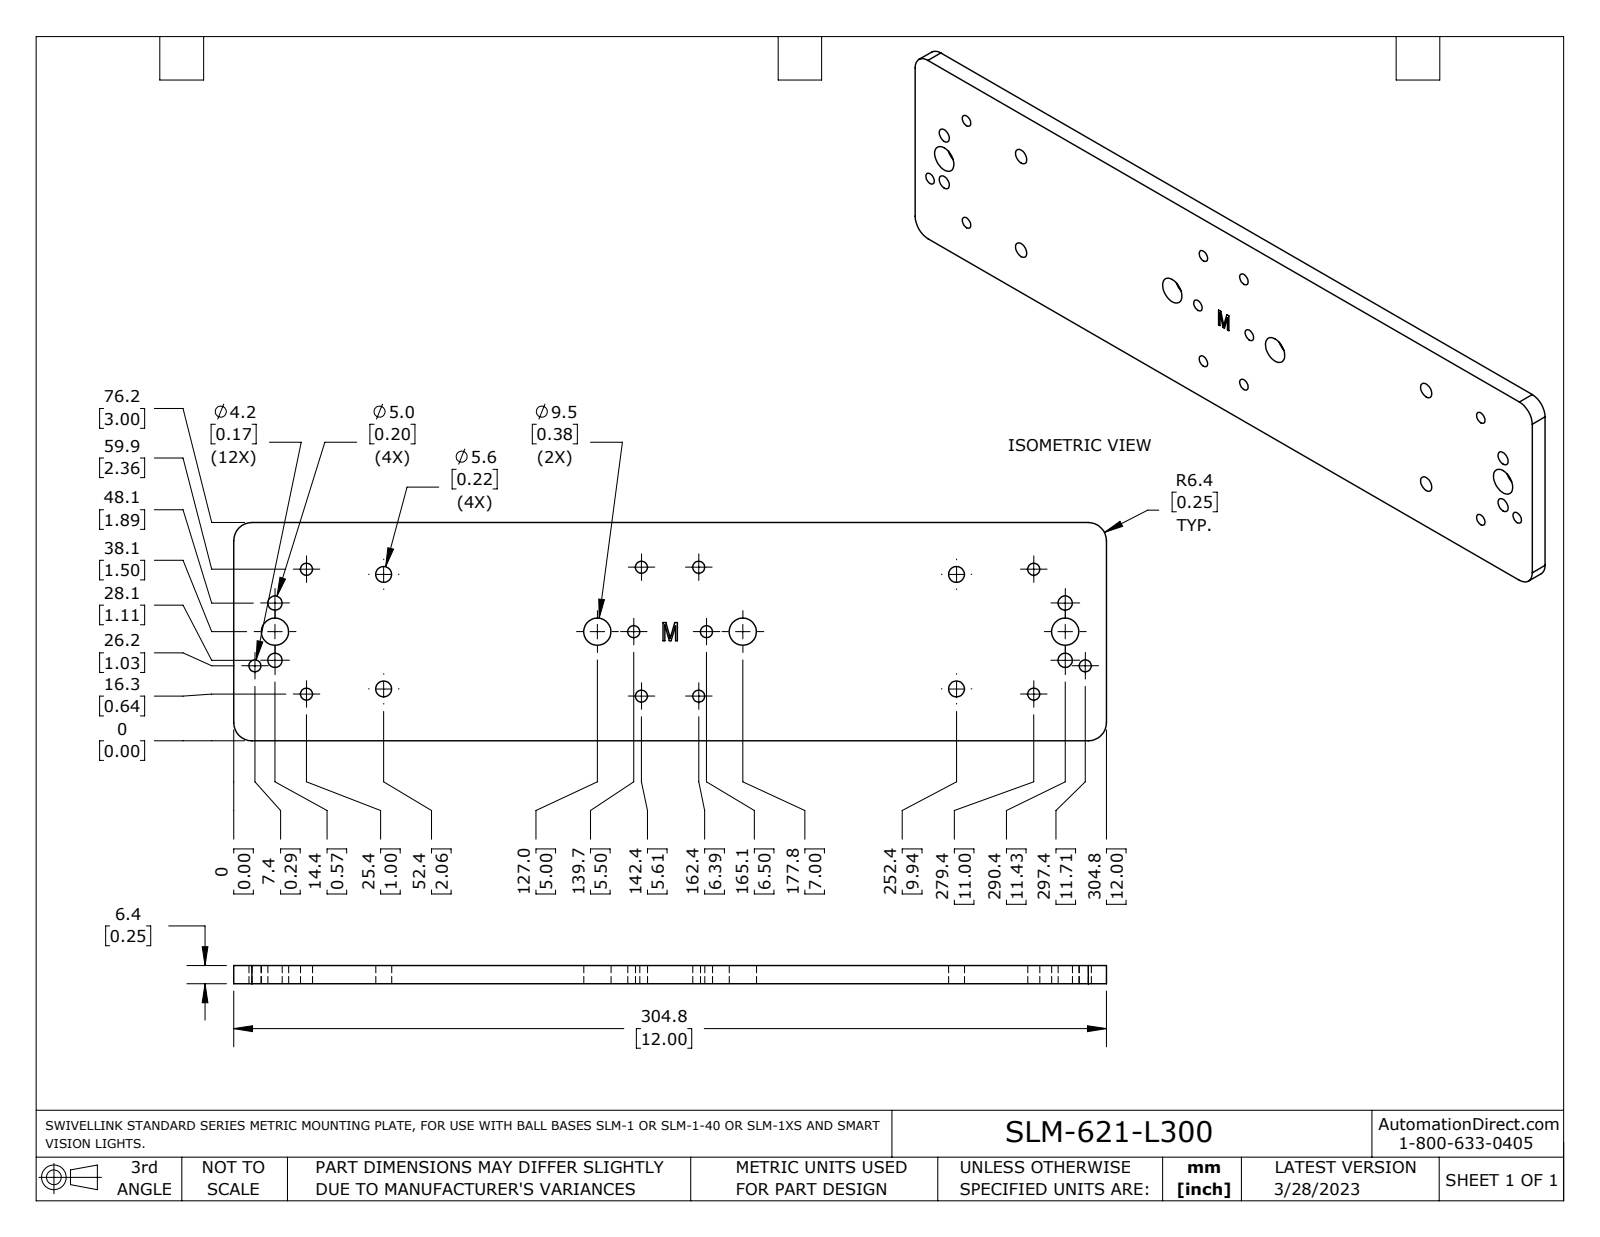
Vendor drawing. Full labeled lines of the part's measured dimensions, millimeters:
Part name (STEP PRODUCT): SLM-621-L300
STEP written by: SolidWorks 2021 (AUTOMOTIVE_DESIGN)
Units: millimetres
Bodies: 1 solid, 35 faces (7 planar, 28 cylindrical, 0 other)
Overall size (bounding box): 304.8 × 76.2 × 6.4
Volume: 143 300 mm³ · Surface area: 52 500 mm²
Round holes (diameter × count): ⌀4.2 ×12, ⌀5 ×4, ⌀5.6 ×4, ⌀9.5 ×2, ⌀9.5 ×2
Partial cylindrical surfaces — rounded edges, fillets, slot ends (radius × count): R6.4 ×4
Main face-to-face distances: 6.4, 76.2, 304.8
Hole centre spacings: 10, 16.1, 20, 22.7, 24.4, 27, 27.3, 32
